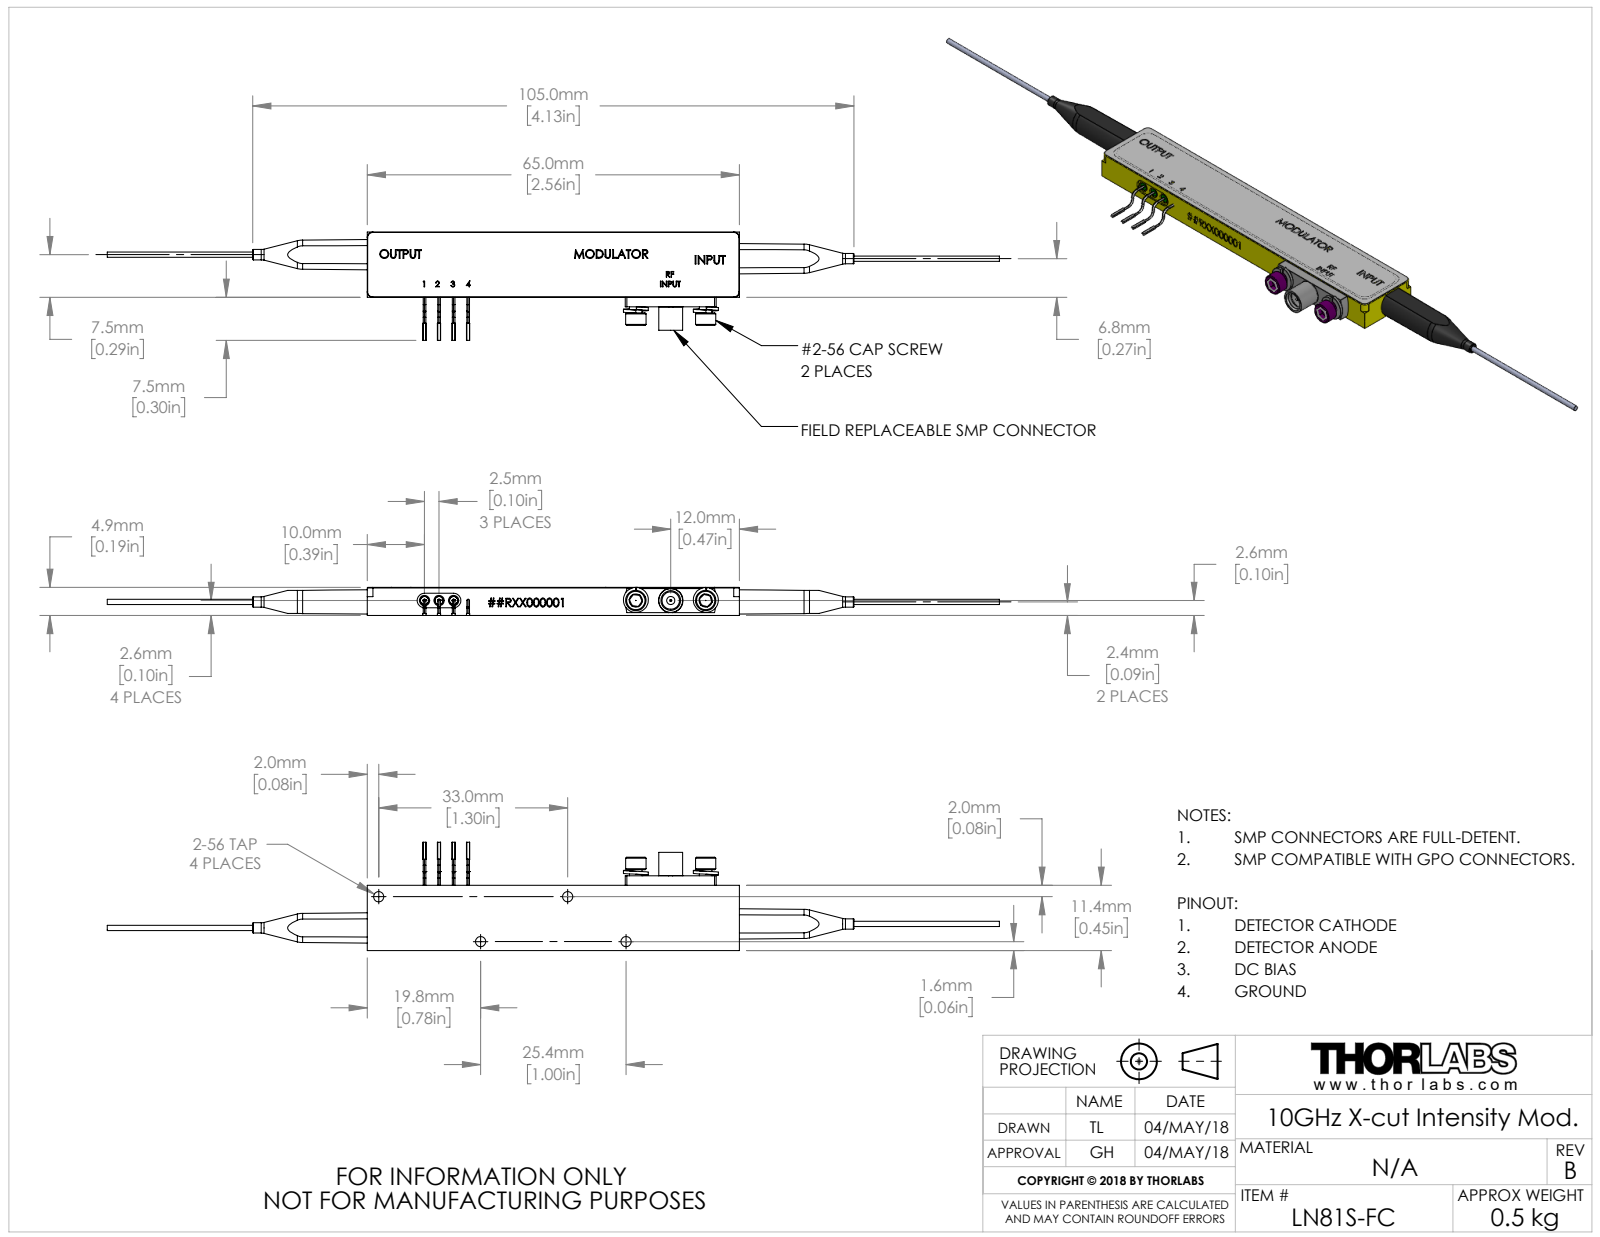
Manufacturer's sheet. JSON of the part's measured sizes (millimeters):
{"part_name": "19524-E0W", "step_written_by": "SolidWorks 2016 (CONFIG_CONTROL_DESIGN)", "units": "millimeters", "bodies": {"solids": 0, "faces": 458, "planar": 211, "cylindrical": 115, "other": 132}, "overall_size": [155.8, 18.89, 4.91], "round_holes": [[1.78, 4], [1.8, 3], [2.61, 1], [3.05, 1], [3.18, 1]], "round_bosses_or_shafts": [[0.46, 4], [3.56, 2], [2.18, 2], [1.8, 2], [0.9, 2], [4.16, 1], [1.45, 1], [0.38, 1]], "partial_cylinders_radius": [[0.23, 12], [0.9, 4], [1, 4], [1.27, 2], [7.93, 1]], "face_to_face_distances": [4.91, 11.4, 4.78, 4.83, 65, 1.65, 13.05, 0.5, 4.7, 4.2], "hole_center_spacings": [2.54, 5.08, 6.1, 12.86, 17.1, 19.45, 25.4, 33]}
